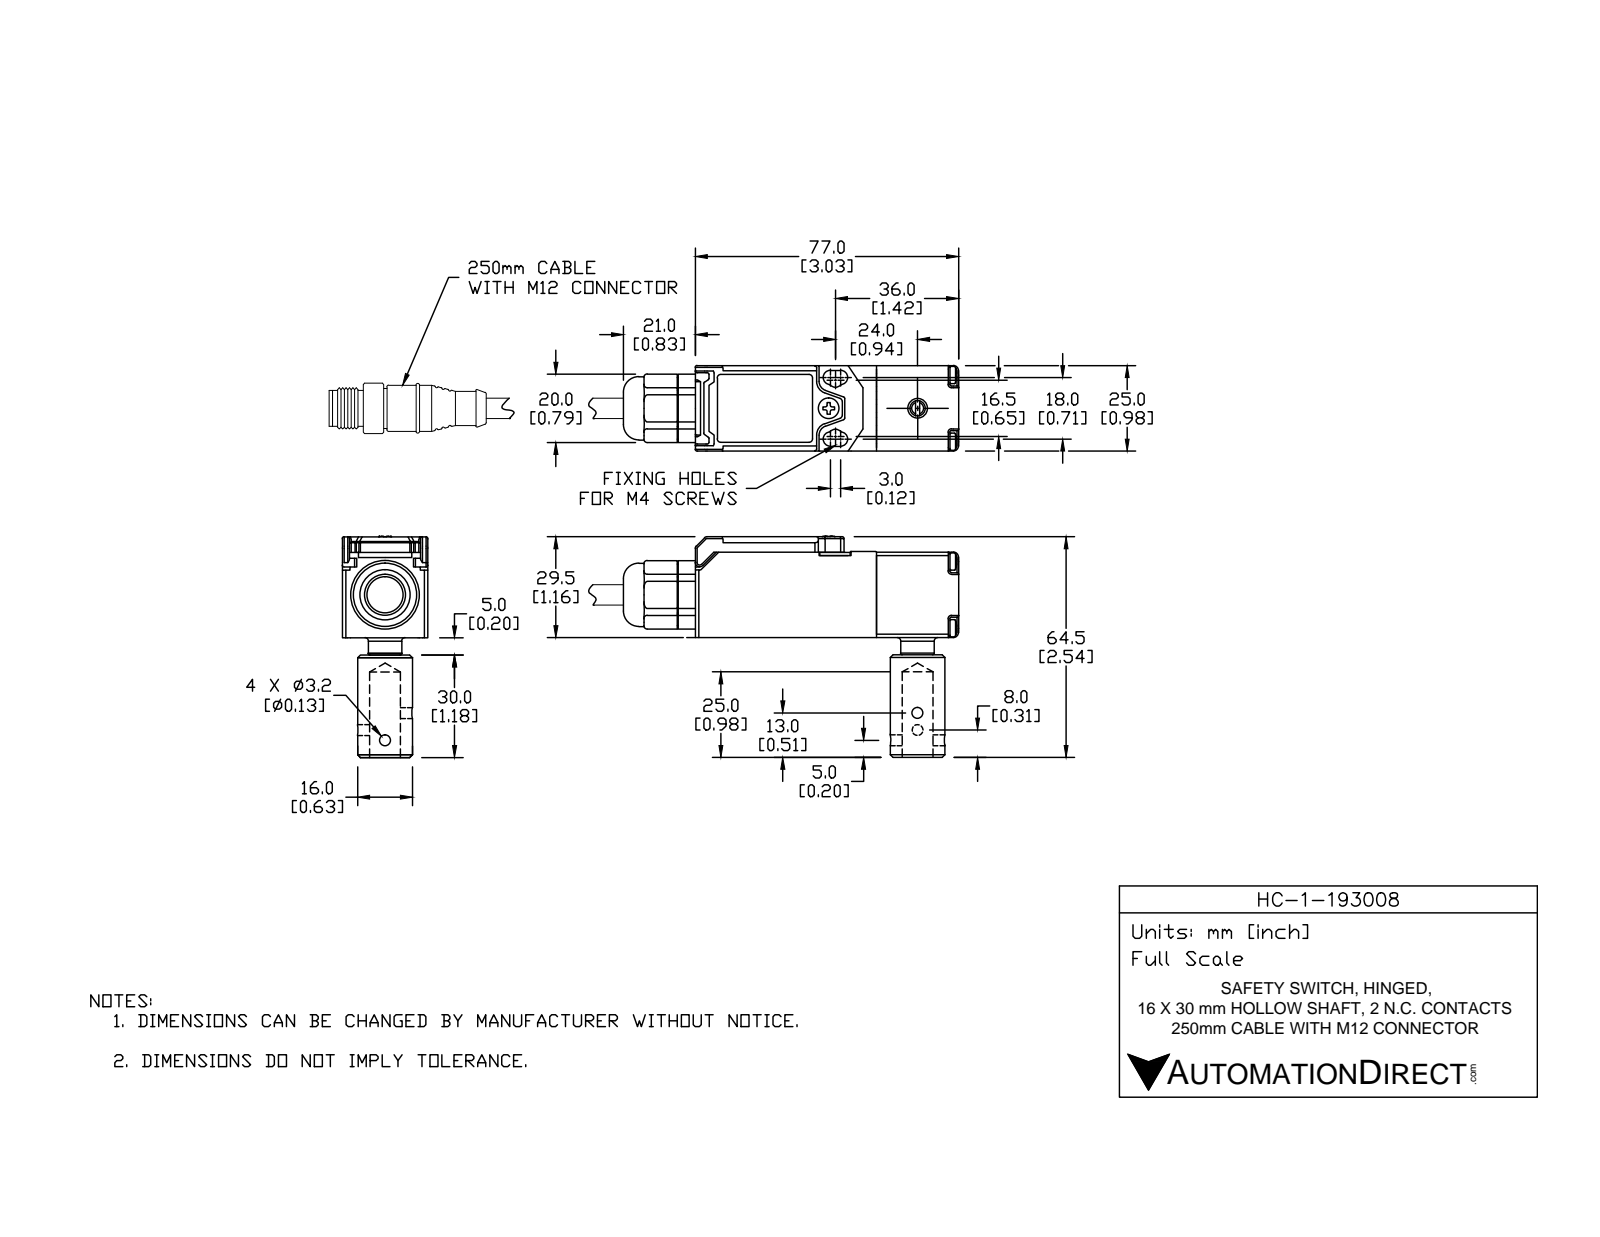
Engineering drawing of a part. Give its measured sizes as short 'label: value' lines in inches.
name: HC-1-193008
written by: SolidWorks 2014 (AUTOMOTIVE_DESIGN)
unit: in
bodies: 14 solids, 1716 faces (700 planar, 611 cylindrical, 405 other)
size: 3.169 × 2.549 × 0.984
volume: 1.796 in³; area: 44.56 in²
holes: 8× ⌀0.126, 4× ⌀0.094, 2× ⌀0.059, 2× ⌀0.063, 2× ⌀0.071, 2× ⌀0.087, 2× ⌀0.142, 1× ⌀0.055, 1× ⌀0.081, 1× ⌀0.098, 1× ⌀0.102, 1× ⌀0.185
bosses: 5× ⌀0.102, 4× ⌀0.197, 4× ⌀0.079, 2× ⌀0.138, 1× ⌀0.74, 1× ⌀0.63, 1× ⌀0.531, 1× ⌀0.386
rounds: 226× R0.02, 24× R0.004, 20× R0.012, 20× R0.039, 7× R0.059, 6× R0.083, 6× R0.11, 4× R0.008
face distances: 0.984, 0.079, 0.071, 0.913, 0.039, 0.906, 0.945, 0.827, 0.874, 1.15
hole spacings: 0.543, 0.768, 0.171, 0.187, 0.245, 0.414, 0.423, 0.426
